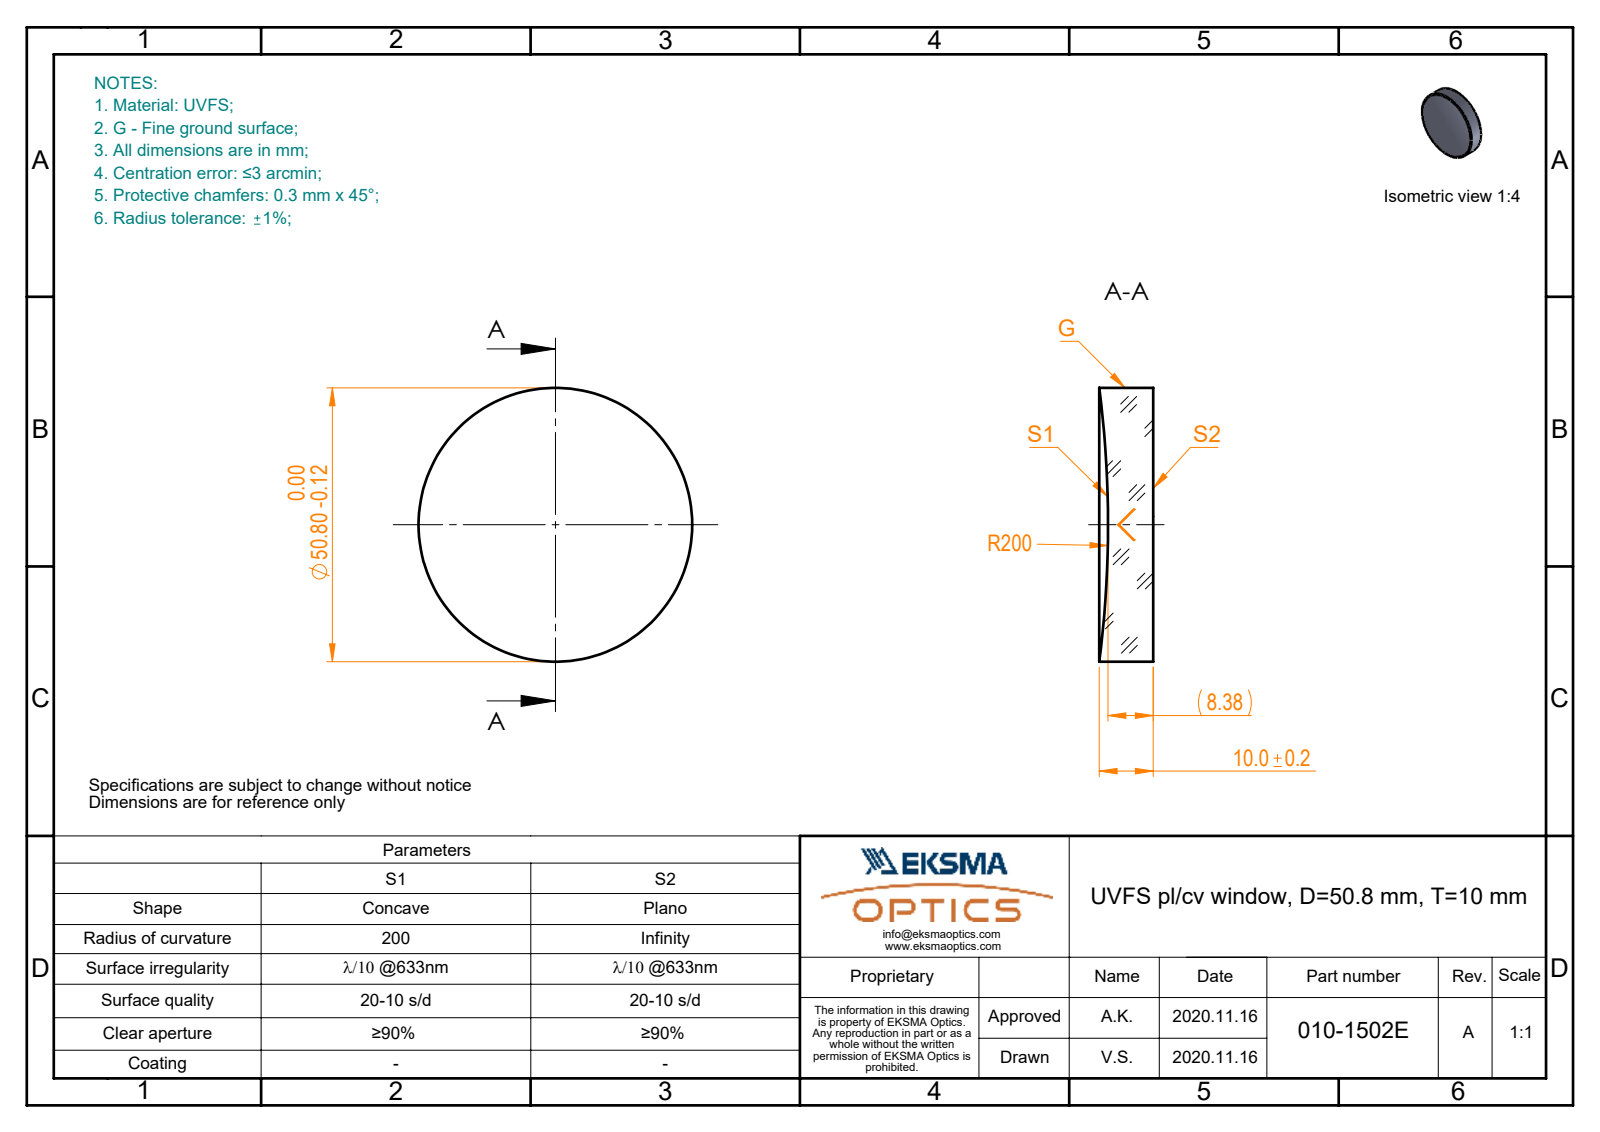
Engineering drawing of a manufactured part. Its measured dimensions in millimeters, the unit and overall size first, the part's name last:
Units: millimetres
Overall size (bounding box): 50.8 × 50.8 × 10
Round bosses / shafts (diameter × count): ⌀50.8 ×1
Volume: 18 625 mm³ · Surface area: 5 658 mm²
Bodies: 1 solid, 5 faces (1 planar, 2 cylindrical, 2 other)
Part name (STEP PRODUCT): 010-1502E_UVFS_PCV_window
STEP written by: SolidWorks 2019 (CONFIG_CONTROL_DESIGN)
